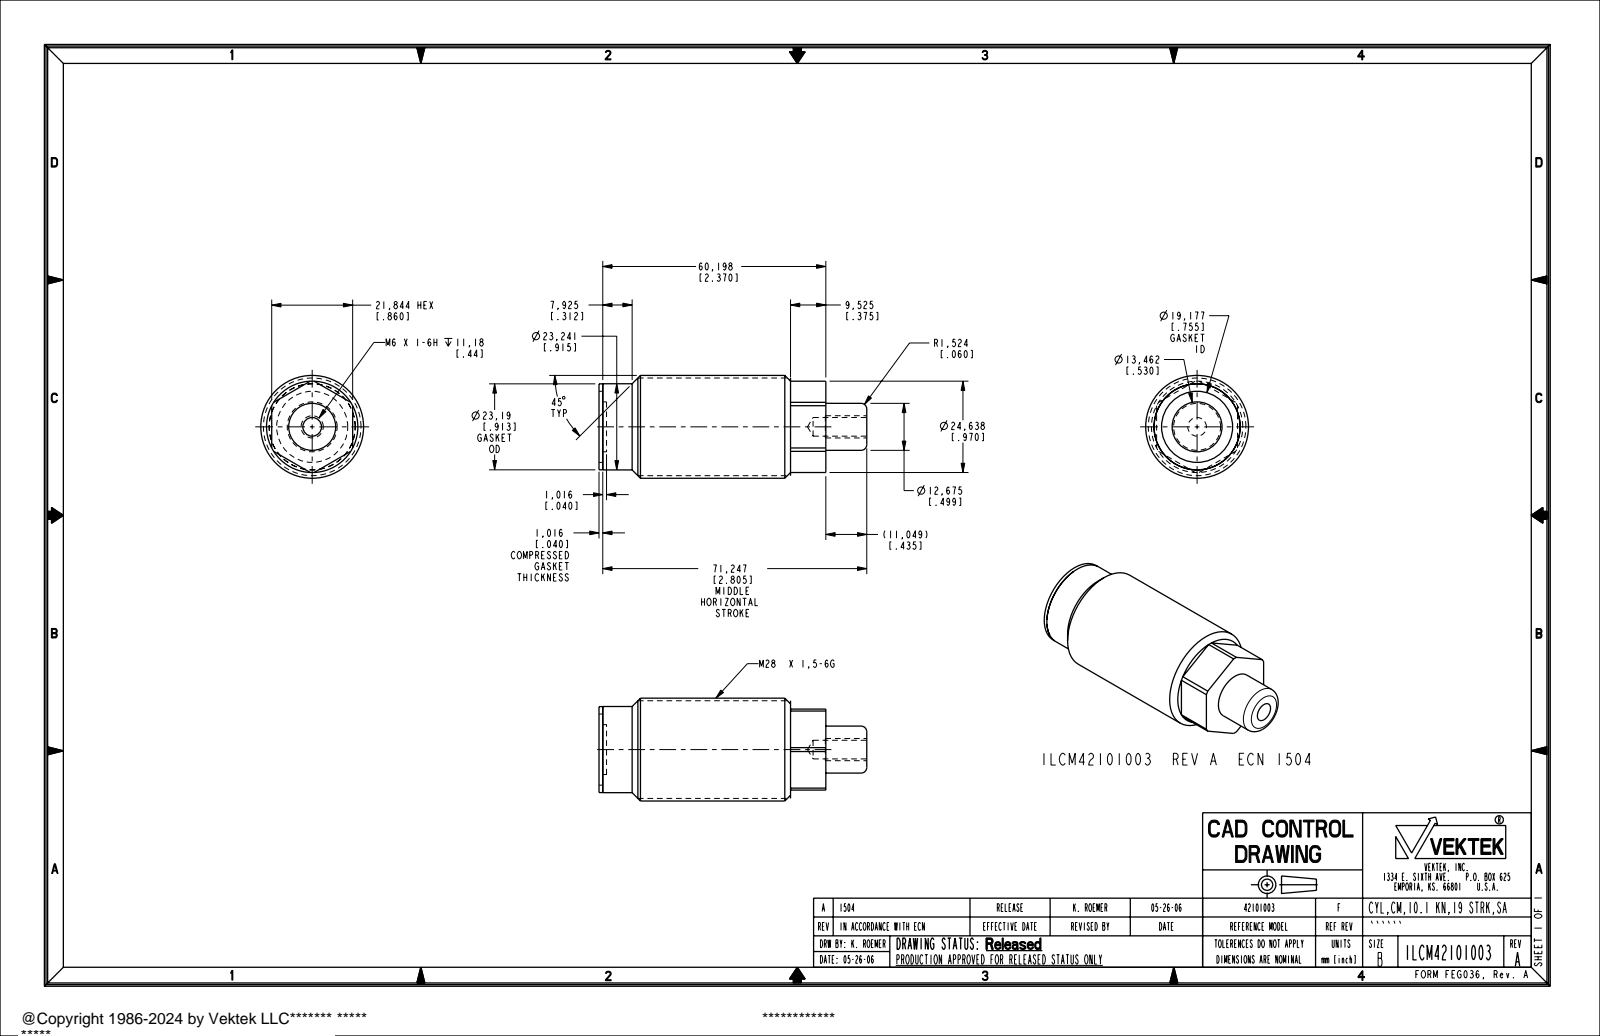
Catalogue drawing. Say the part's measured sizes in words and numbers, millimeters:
The part is named "ILCM42101003". Its 3-D file was written by "PRO/ENGINEER BY PARAMETRIC TECHNOLOGY CORPORATION, 2004290 (AUTOMOTIVE_DESIGN_CC2)". It is 2 solids with 52 faces: 20 planar, 24 cylindrical and 8 other. Overall it measures 72.26 by 27.74 by 27.74 millimeters. Its volume is 33 875 cubic millimeters and its surface area 11 280 square millimeters. Round holes: 1 of diameter 5.03, 1 of diameter 13.46, 1 of diameter 19.18. Round bosses or shafts: 1 of diameter 27.74, 1 of diameter 26.34, 1 of diameter 23.24, 1 of diameter 23.19, 1 of diameter 12.67, 1 of diameter 5.99. Partial cylindrical surfaces (rounded edges, fillets, slot ends): 1 of radius 12.32. The main face-to-face distances are 21.84, 9.53, 50.67, 60.2, 1.02, 49.65, 59.18, 0.99, 2.04, 51.69.
